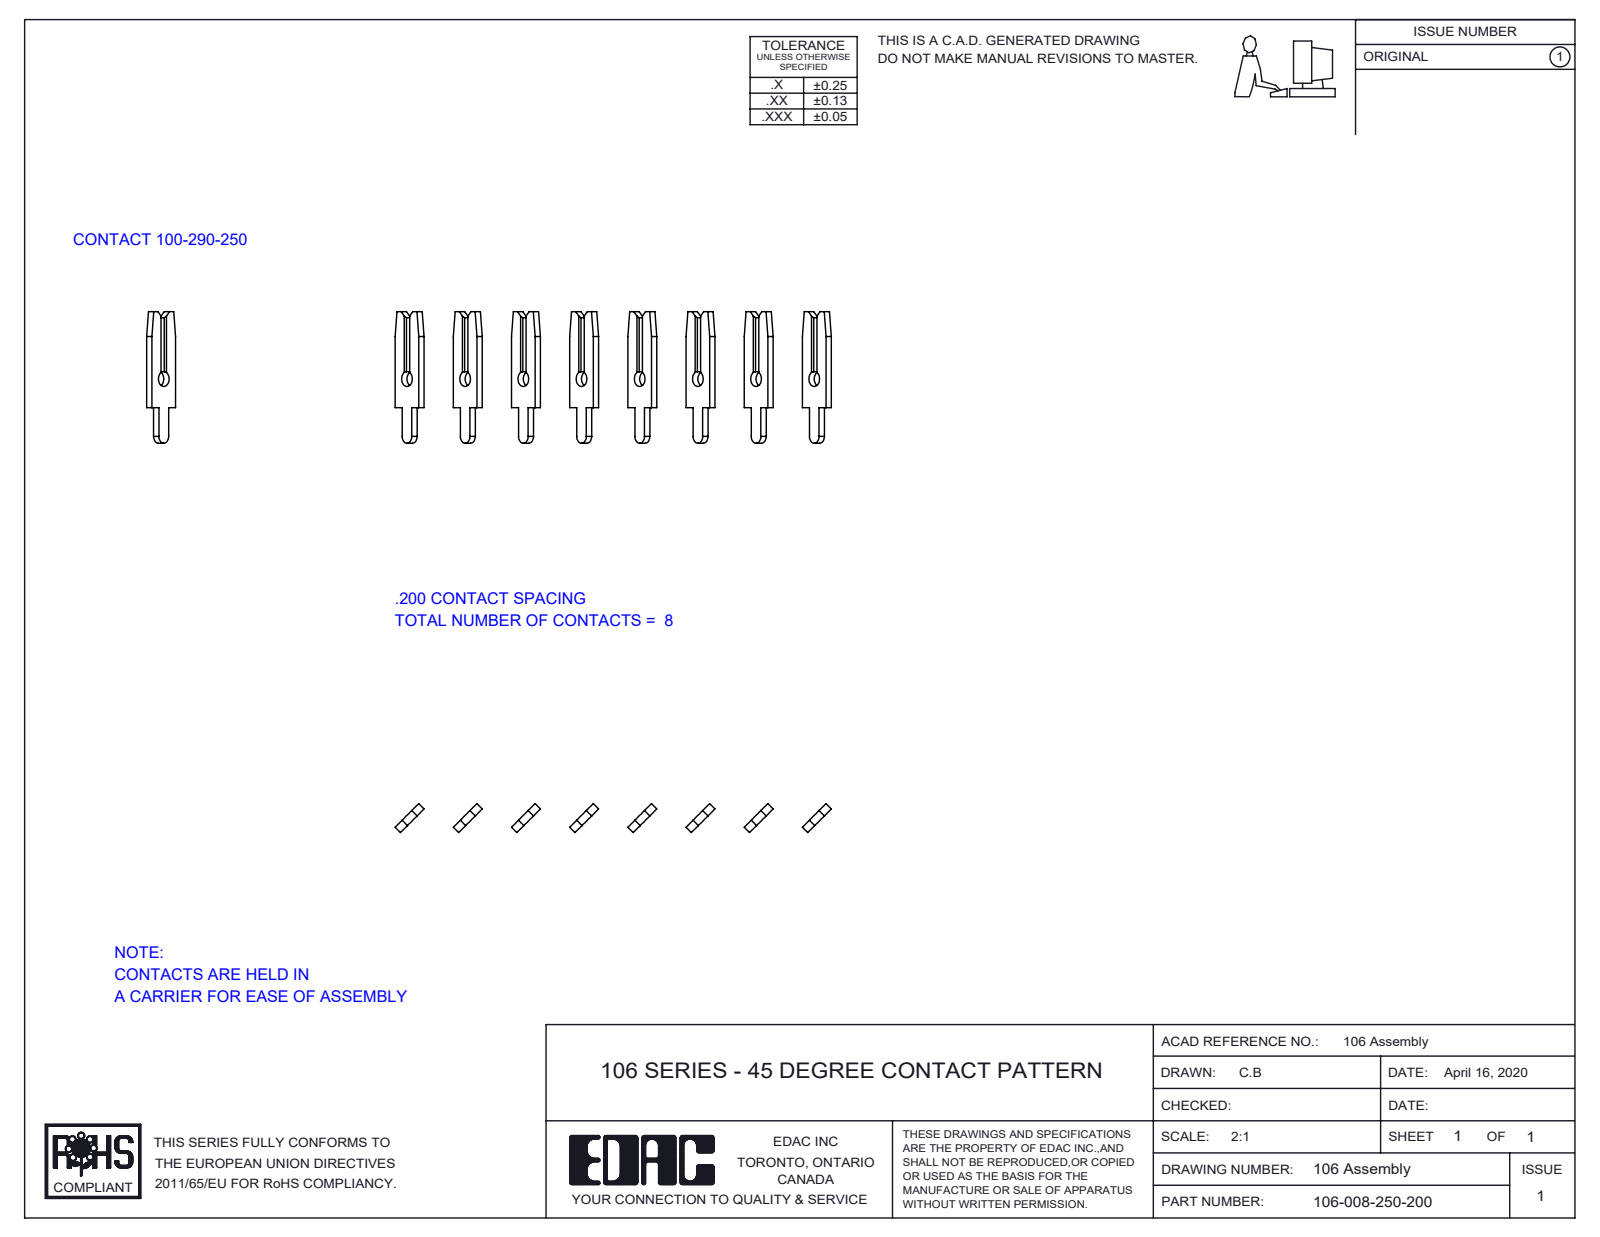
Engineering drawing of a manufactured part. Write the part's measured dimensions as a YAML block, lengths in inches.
part_name: "100-290-001_100-290-250; 106-008-250-200"
step_written_by: "SolidWorks 2016 (CONFIG_CONTROL_DESIGN)"
units: inches
bodies: {solids: 8, faces: 192, planar: 160, cylindrical: 32, other: 0}
overall_size: [1.5, 0.452, 0.1]
volume: 0.008
surface_area: 0.91
round_holes:
  - {diameter: 0.052, count: 8}
partial_cylinders:
  - {radius: 0.024, count: 8}
face_to_face_distances: [0.141, 0.283, 0.026, 0.566, 0.707, 0.424, 0.115, 0.167, 0.424, 0.848]
hole_center_spacings: [0.141, 0.424, 0.283, 0.566, 0.707, 0.283, 0.849, 0.142]
